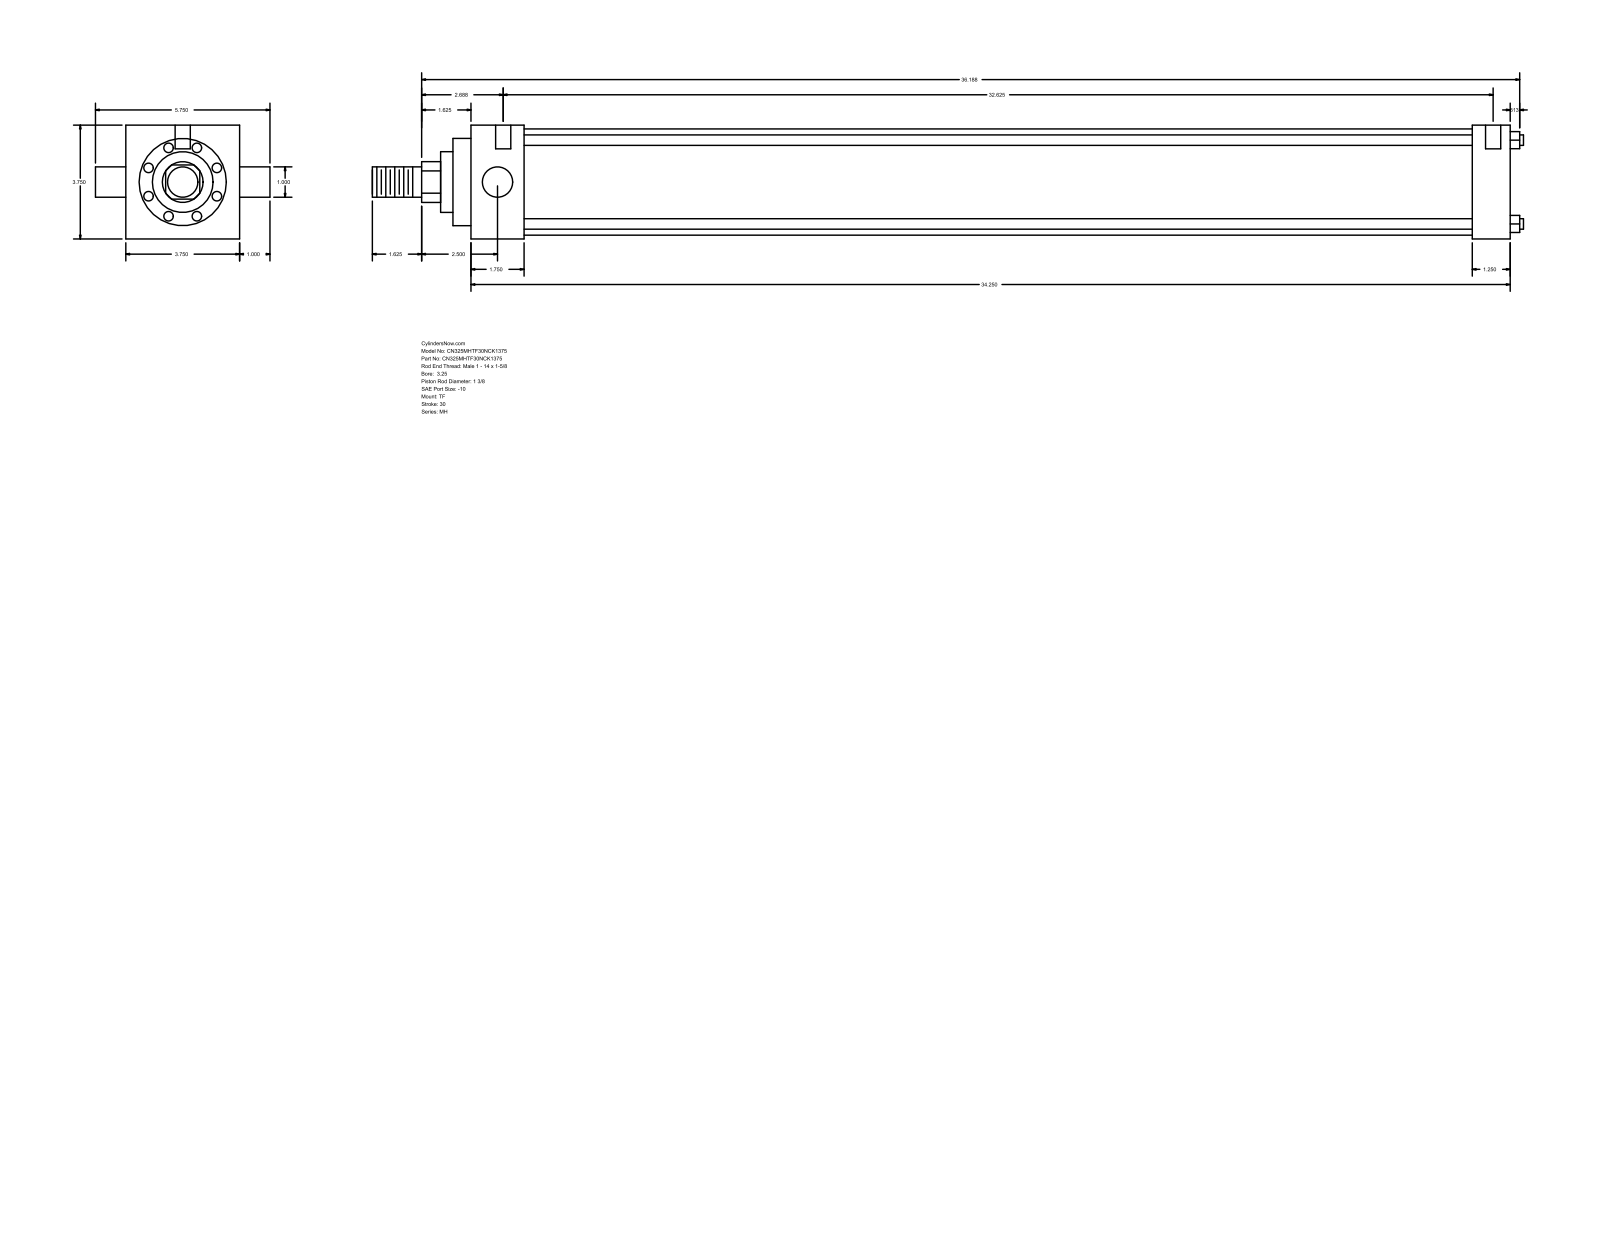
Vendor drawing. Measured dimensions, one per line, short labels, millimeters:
name: MH_TF__0325_1.375
written by: GSSL Pune (CONFIG_CONTROL_DESIGN)
unit: mm
bodies: 0 solids, 86 faces (61 planar, 25 cylindrical, 0 other)
size: 963.61 × 146.05 × 95.25
holes: 3× ⌀5.56, 2× ⌀12.7
bosses: 4× ⌀8.76, 2× ⌀25.4, 1× ⌀88.9, 1× ⌀73.03, 1× ⌀50.8, 1× ⌀34.92
rounds: 1× R17.06
face distances: 95.24, 869.96, 44.45, 838.21, 793.76, 825.51, 31.75, 15.08, 59.53, 853.29
hole spacings: 1.59, 4.76, 828.68, 830.27, 833.44, 835.03
